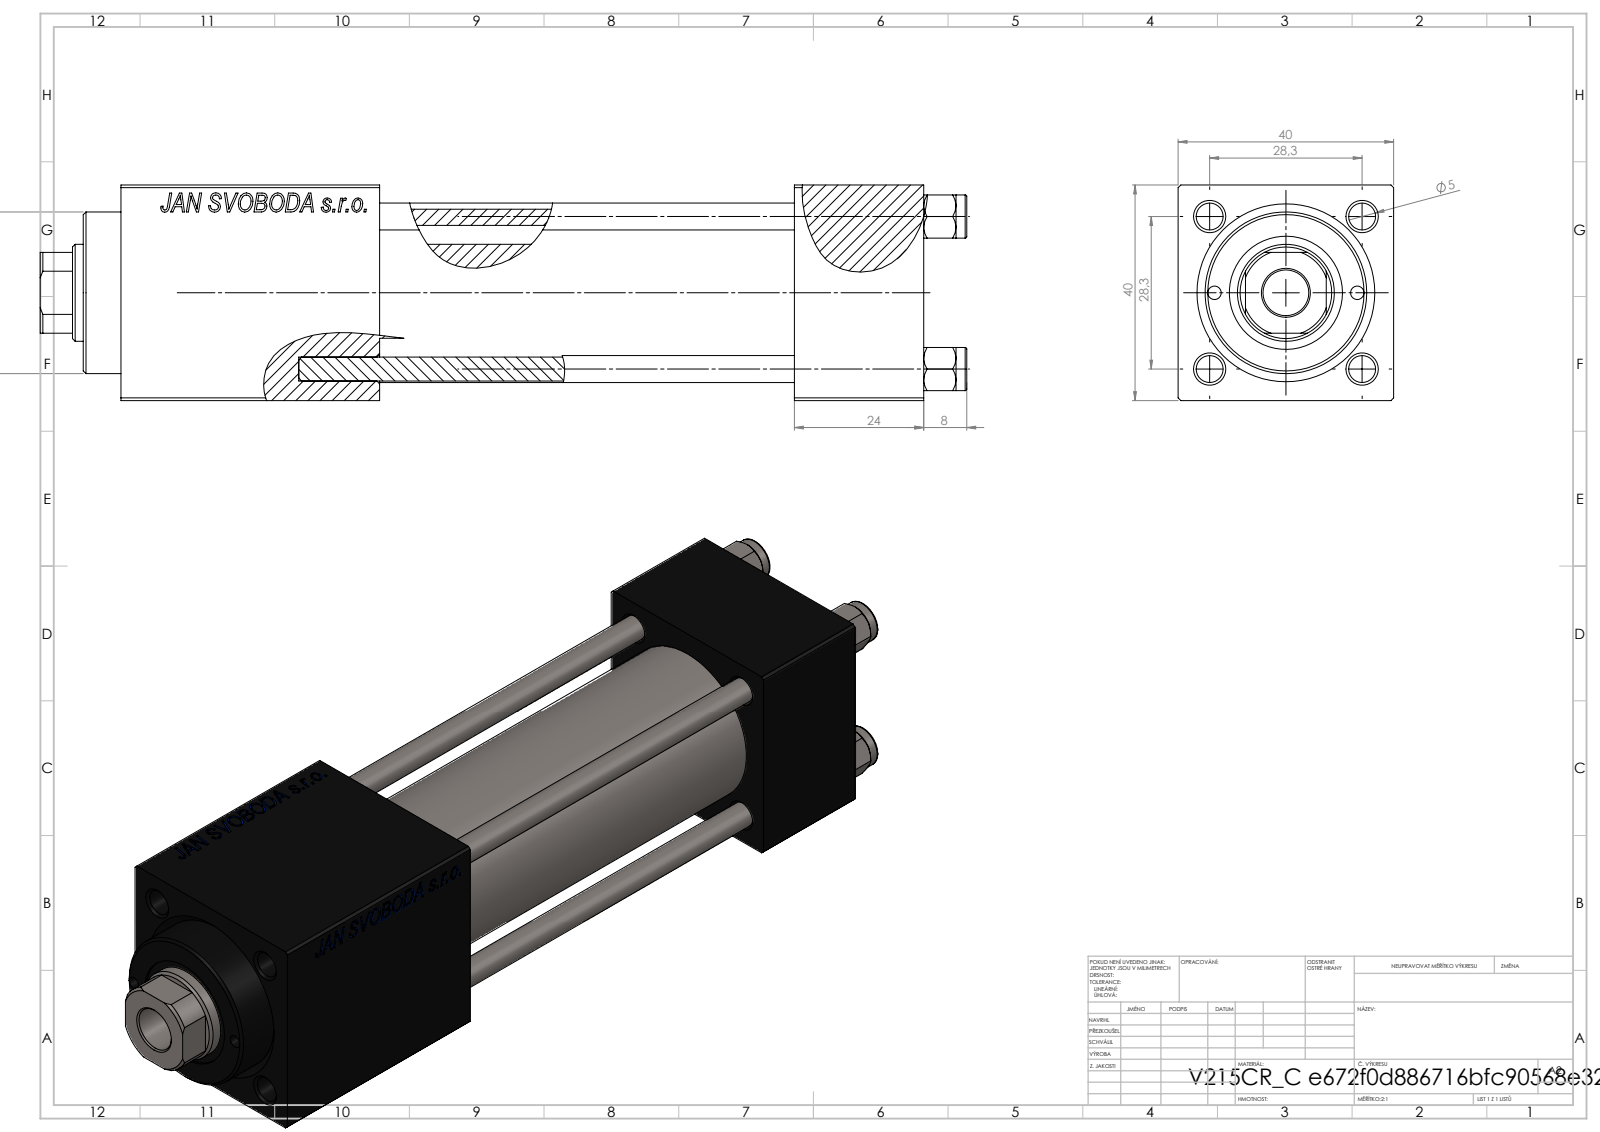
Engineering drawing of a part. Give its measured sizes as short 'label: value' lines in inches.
name: V215CR_C_TYCINKA; NUT_M5_C; V215CR_C_Body; V215CR_VCP_C (+1 more)
written by: SolidWorks 2019 (CONFIG_CONTROL_DESIGN)
unit: in
bodies: 11 solids, 1150 faces (526 planar, 88 cylindrical, 536 other)
size: 6.772 × 1.575 × 1.575
volume: 10.24 in³; area: 101.9 in²
holes: 4× ⌀0.197, 3× ⌀0.787, 2× ⌀0.098, 2× ⌀0.276, 2× ⌀0.518, 1× ⌀0.335, 1× ⌀0.709, 1× ⌀0.827, 1× ⌀0.984, 1× ⌀1.181
bosses: 4× ⌀0.315, 1× ⌀1.22
rounds: 1× R0.335
face distances: 1.575, 0.945, 3.976, 3.031, 4.736, 3.791, 0.76, 1.89, 5.866, 4.921
hole spacings: 0.558, 0.788, 1.114, 1.214, 0.522, 1.576, 1.043, 4.016
